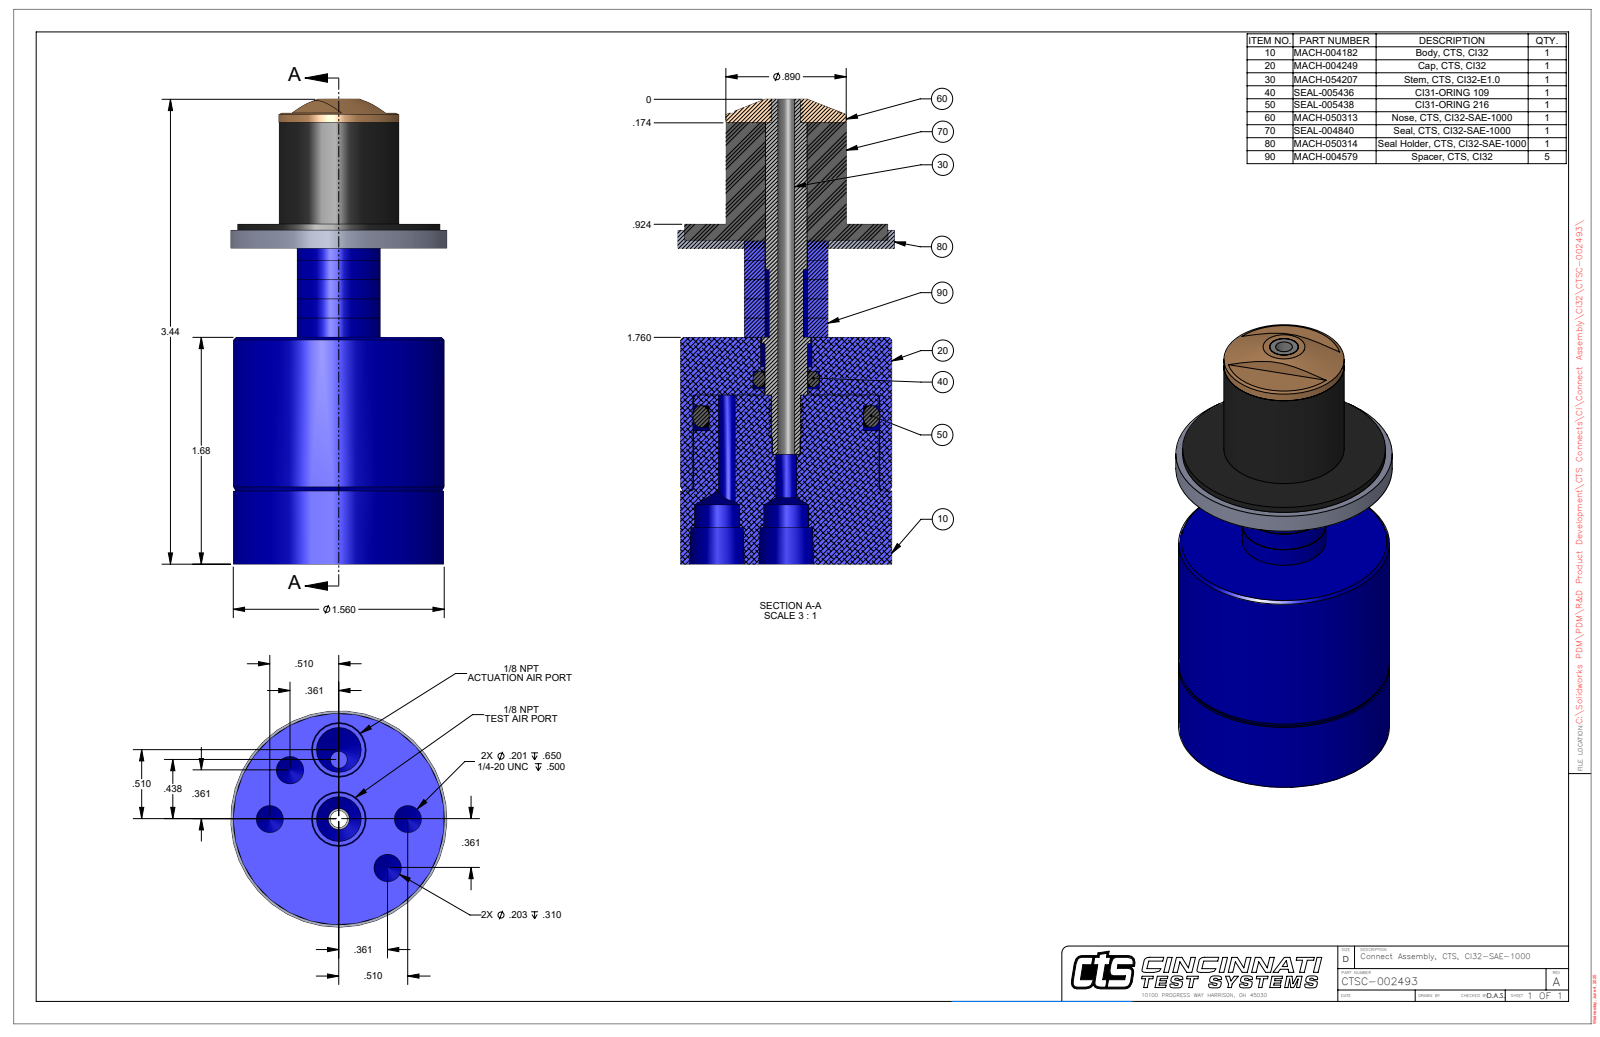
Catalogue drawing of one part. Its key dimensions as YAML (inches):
part_name: "CTSC-002493"
step_written_by: "SolidWorks 2023 (AUTOMOTIVE_DESIGN)"
units: inches
bodies: {solids: 1, faces: 102, planar: 27, cylindrical: 44, other: 31}
overall_size: [3.437, 1.6, 1.6]
volume: 4.063
surface_area: 27.51
round_holes:
  - {diameter: 0.125, count: 2}
  - {diameter: 0.201, count: 2}
  - {diameter: 0.203, count: 2}
  - {diameter: 0.332, count: 2}
  - {diameter: 0.156, count: 1}
  - {diameter: 0.213, count: 1}
  - {diameter: 0.314, count: 1}
  - {diameter: 0.38, count: 1}
  - {diameter: 1.377, count: 1}
round_bosses_or_shafts:
  - {diameter: 1.6, count: 1}
  - {diameter: 1.56, count: 1}
  - {diameter: 1.5, count: 1}
  - {diameter: 1.365, count: 1}
  - {diameter: 0.89, count: 1}
  - {diameter: 0.618, count: 1}
  - {diameter: 0.357, count: 1}
  - {diameter: 0.31, count: 1}
face_to_face_distances: [0.656, 1.677, 2.333, 2.513, 0.836, 0.18, 1.656, 0.865, 3.333, 1]
hole_center_spacings: [0.51, 0.39, 0.942, 0.672, 0.721, 0.072, 0.369, 0.437]
